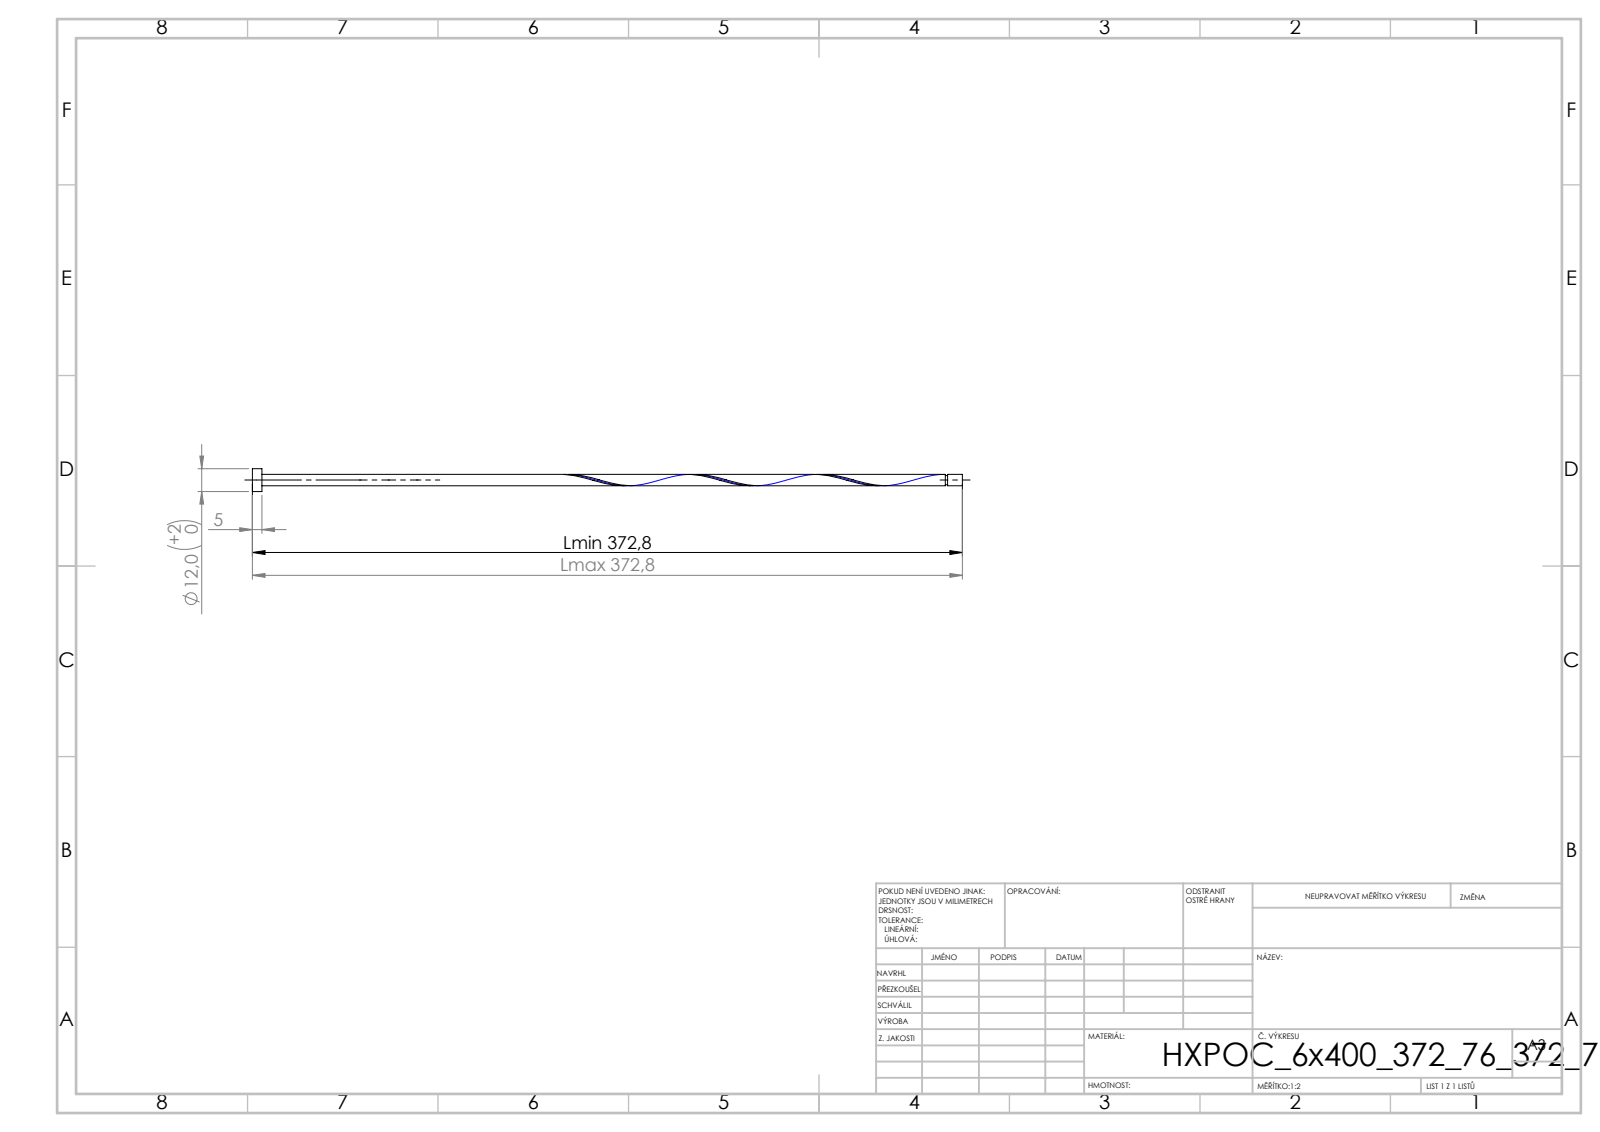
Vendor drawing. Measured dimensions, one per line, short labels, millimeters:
written by: SolidWorks 2019 (CONFIG_CONTROL_DESIGN)
unit: mm
bodies: 1 solid, 16 faces (6 planar, 9 cylindrical, 1 other)
size: 372.76 × 12 × 12
volume: 13 358 mm³; area: 9 996 mm²
bosses: 1× ⌀12, 1× ⌀6, 1× ⌀4.8
face distances: 5, 372.76, 367.76, 364.97, 359.97, 7.79, 363.77, 358.77, 1.2, 8.99
